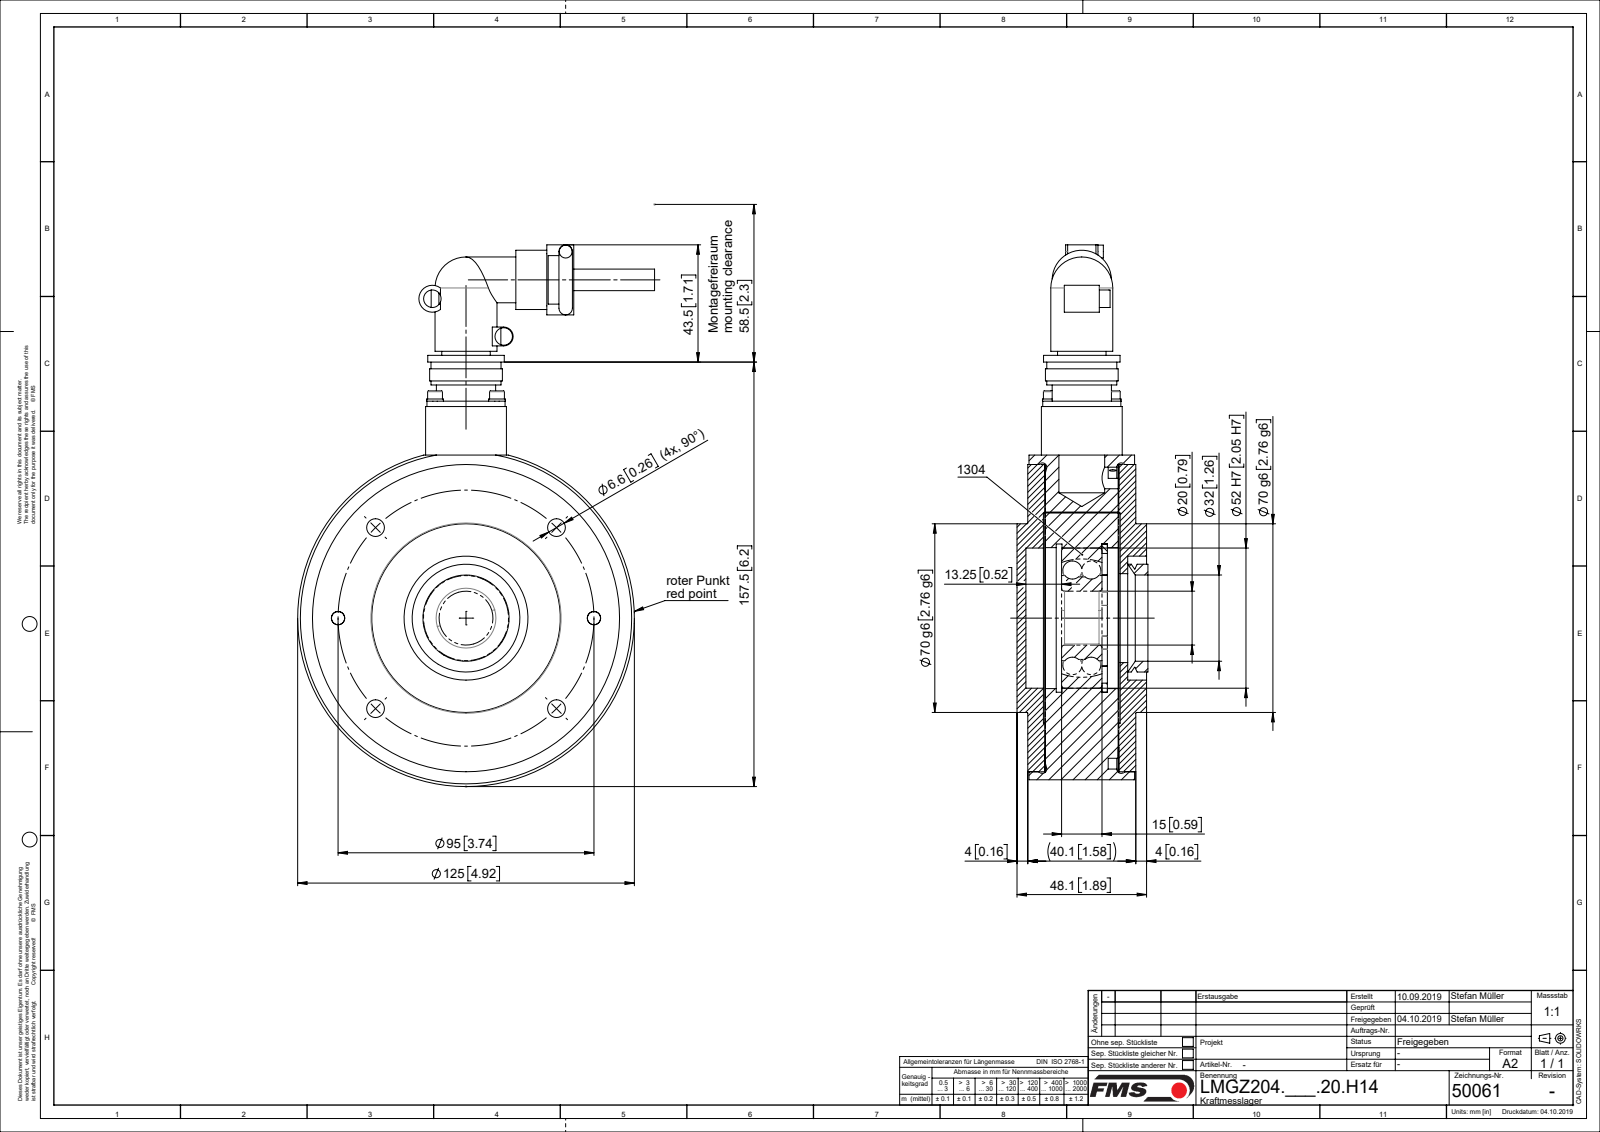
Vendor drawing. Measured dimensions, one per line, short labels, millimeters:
name: ZEICHNUNG7; L50061; L4832404; L47956 (+8 more)
written by: Mechanical Desktop 2007 (CONFIG_CONTROL_DESIGN)
unit: mm
bodies: 20 solids, 412 faces (119 planar, 242 cylindrical, 51 other)
size: 201 × 132.5 × 48.1
volume: 493 636 mm³; area: 146 552 mm²
holes: 6× ⌀6.6, 4× ⌀2.6, 4× ⌀3.2, 4× ⌀3.4, 4× ⌀3.5, 2× ⌀5, 2× ⌀11, 1× ⌀20, 1× ⌀23, 1× ⌀31, 1× ⌀33, 1× ⌀37.9
bosses: 4× ⌀6.2, 4× ⌀5.5, 4× ⌀3, 2× ⌀22, 2× ⌀10, 2× ⌀6.5, 2× ⌀6, 2× ⌀4.8
rounds: 9× R5, 2× R2.5, 1× R3.5, 1× R40.5, 1× R47
face distances: 27.25, 33.55, 6.3, 6.55, 33.8, 27, 27.5, 4, 10.55, 37.8
hole spacings: 47.5, 16.26, 23, 36.36, 67.18, 87.77, 32.53, 95.01
